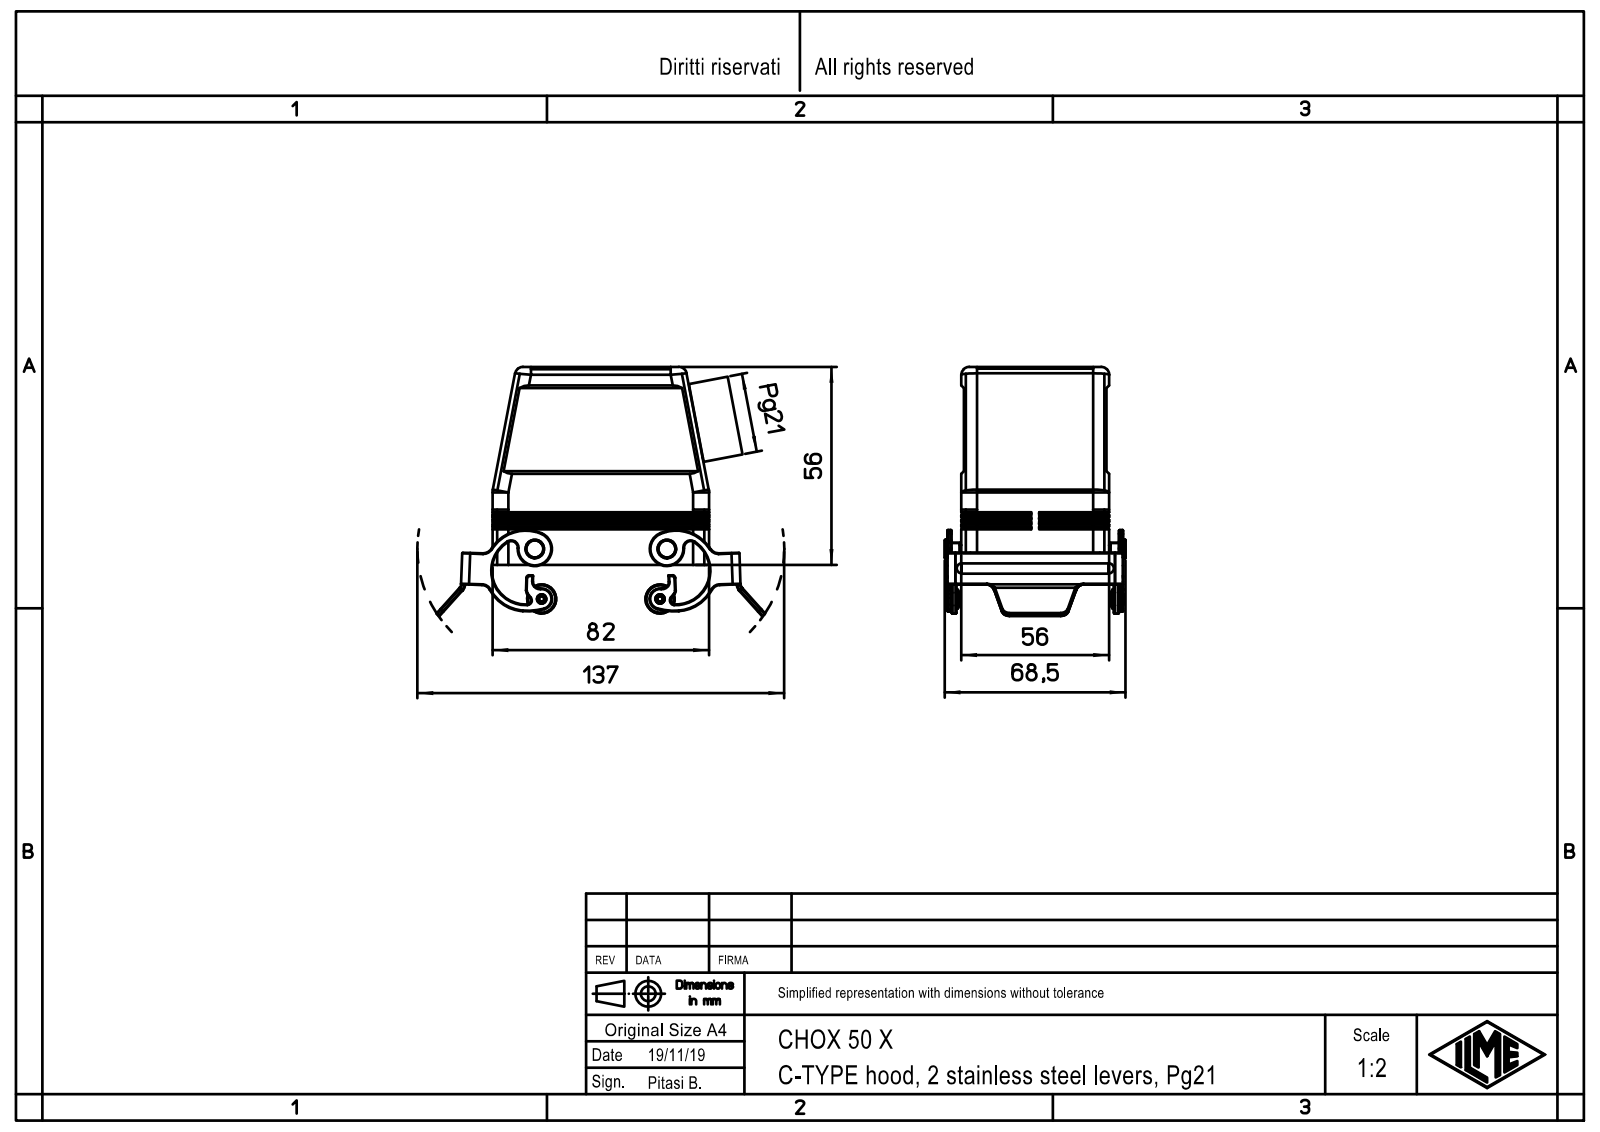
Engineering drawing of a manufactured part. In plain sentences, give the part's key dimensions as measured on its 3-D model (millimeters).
The part is named "Leva; CHPX 50.21.1; CHPX 50.21.3; Leva.1 (+4 more)". Its 3-D file was written by "Creo Elements/Direct Modeling 20.1B 02-Apr-2019 (C) Parametric Technology GmbH (AUTOMOTIVE_DESIGN)". It is 7 solids with 587 faces: 219 planar, 238 cylindrical and 130 other. Overall it measures 124.33 by 82.61 by 68.5 millimeters. Its volume is 78 493 cubic millimeters and its surface area 51 935 square millimeters. Round holes: 8 of diameter 3.5, 4 of diameter 5, 2 of diameter 2, 2 of diameter 3.1, 1 of diameter 28. Round bosses or shafts: 4 of diameter 7, 4 of diameter 4.8, 2 of diameter 11, 2 of diameter 3.5, 2 of diameter 3, 1 of diameter 36. Partial cylindrical surfaces (rounded edges, fillets, slot ends): 18 of radius 3, 16 of radius 2, 12 of radius 0.5, 10 of radius 3.5, 7 of radius 6.5, 6 of radius 1.5, 4 of radius 2.5, 4 of radius 4. The main face-to-face distances are 2.9, 1.5, 65, 7.91, 10.81, 103.41, 66.5, 52.64, 55.54, 10.83. The hole center spacings are 16, 24.2, 66, 67.91, 70.3, 8.2, 19.08, 40.2.
